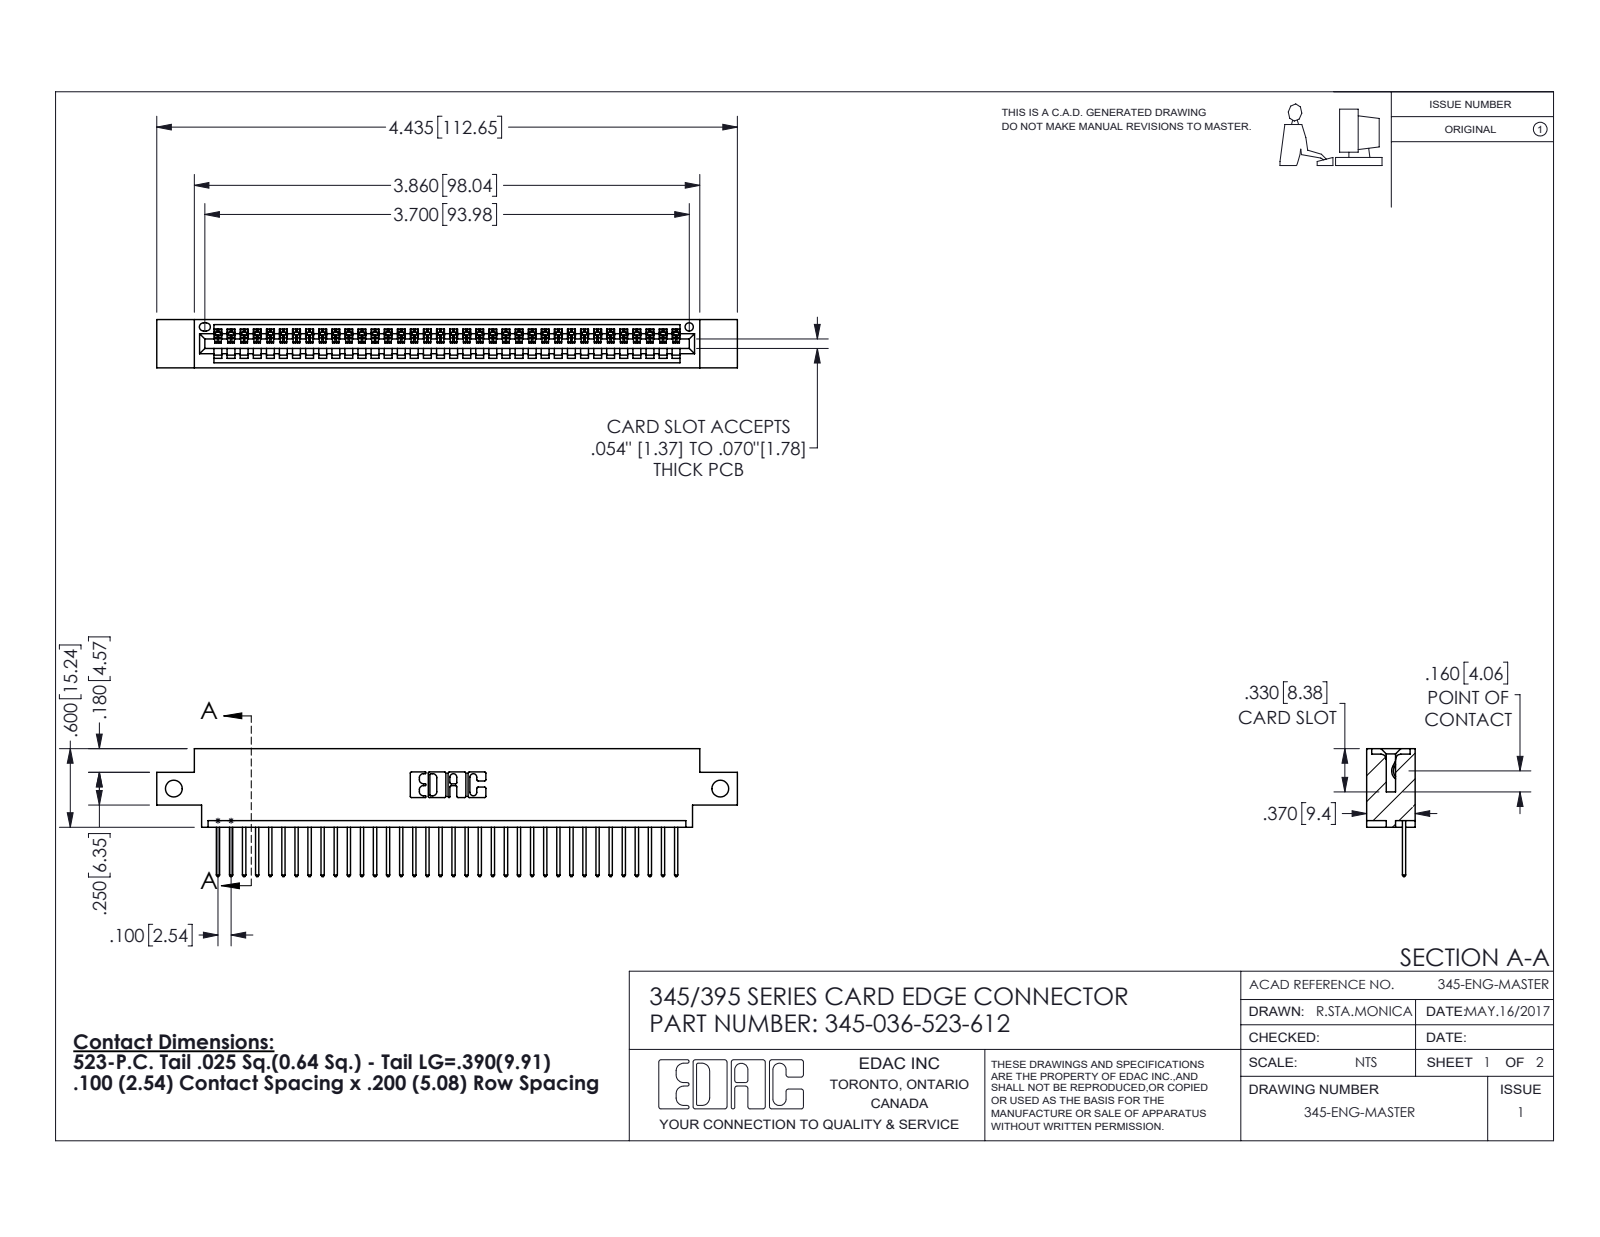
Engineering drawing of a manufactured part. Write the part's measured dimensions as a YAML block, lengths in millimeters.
part_name: "345-036-523-612; 345-292-001_345-293-123; 345 Part_0.170 Offset - Side Mount"
step_written_by: "SolidWorks 2016 (CONFIG_CONTROL_DESIGN)"
units: millimeters
bodies: {solids: 37, faces: 2218, planar: 1524, cylindrical: 694, other: 0}
overall_size: [112.6, 24.8, 9.4]
volume: 10400
surface_area: 13810
round_holes:
  - {diameter: 3.3, count: 2}
  - {diameter: 1.6, count: 1}
partial_cylinders:
  - {radius: 0.2, count: 72}
  - {radius: 0.3, count: 72}
  - {radius: 0.3, count: 22}
  - {radius: 0.2, count: 6}
  - {radius: 0.8, count: 6}
  - {radius: 0.7, count: 3}
  - {radius: 0.8, count: 2}
  - {radius: 1, count: 2}
face_to_face_distances: [7.6, 1.8, 9.4, 5.1, 2.5, 6.9, 0.6, 5.7, 4.4, 3.8]
hole_center_spacings: [106]
